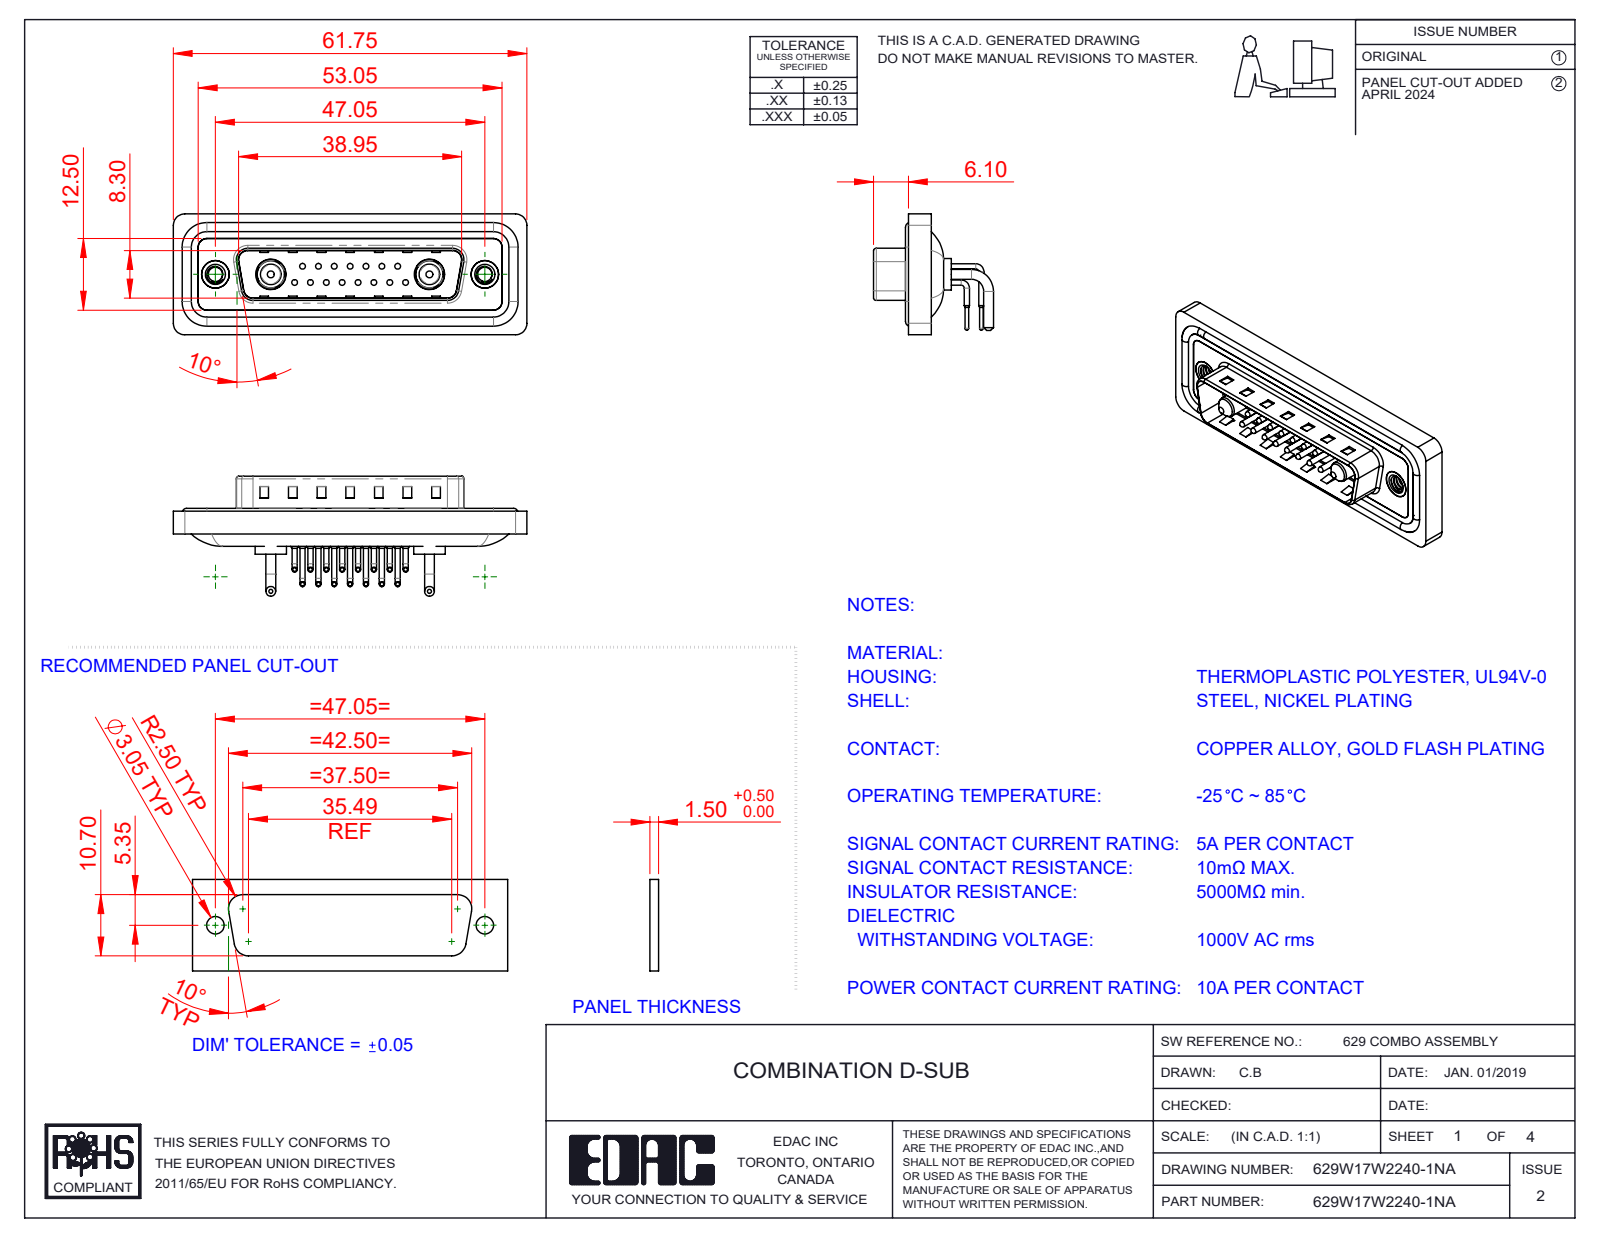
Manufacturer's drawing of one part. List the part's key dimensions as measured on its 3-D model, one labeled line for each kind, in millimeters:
Part name (STEP PRODUCT): Power Pin_10A RA; 629Combo Shell Rear_25 Contacts; 629Combo Housing_17W2; 629Combo Shell Front_25 Contacts (+5 more)
STEP written by: SolidWorks 2023 (CONFIG_CONTROL_DESIGN)
Units: millimetres
Bodies: 26 solids, 2213 faces (1189 planar, 768 cylindrical, 256 other)
Overall size (bounding box): 61.75 × 21.1 × 20.95
Volume: 7 400 mm³ · Surface area: 12 503 mm²
Round holes (diameter × count): ⌀0.75 ×15, ⌀1.6 ×15, ⌀2 ×15, ⌀2.5 ×2, ⌀4 ×2, ⌀4.8 ×2, ⌀4.85 ×2, ⌀5 ×2, ⌀5.3 ×2
Round bosses / shafts (diameter × count): ⌀0.9 ×30, ⌀1.5 ×15, ⌀1 ×15, ⌀0.65 ×15, ⌀1.7 ×4, ⌀1.6 ×4, ⌀5.5 ×2, ⌀5.2 ×2
Partial cylindrical surfaces — rounded edges, fillets, slot ends (radius × count): R1.5 ×18, R2 ×18, R1.01 ×15, R0.5 ×8, R1.6 ×8, R0.25 ×4, R0.6 ×4, R0.65 ×4
Main face-to-face distances: 0.4, 2.9, 0.8, 4.1, 1.1, 2.1, 1.6, 4.5, 1.5, 2.5
Hole centre spacings: 3.16, 2.77, 5.54, 8.31, 5.04, 7.49, 11.08, 5.03
